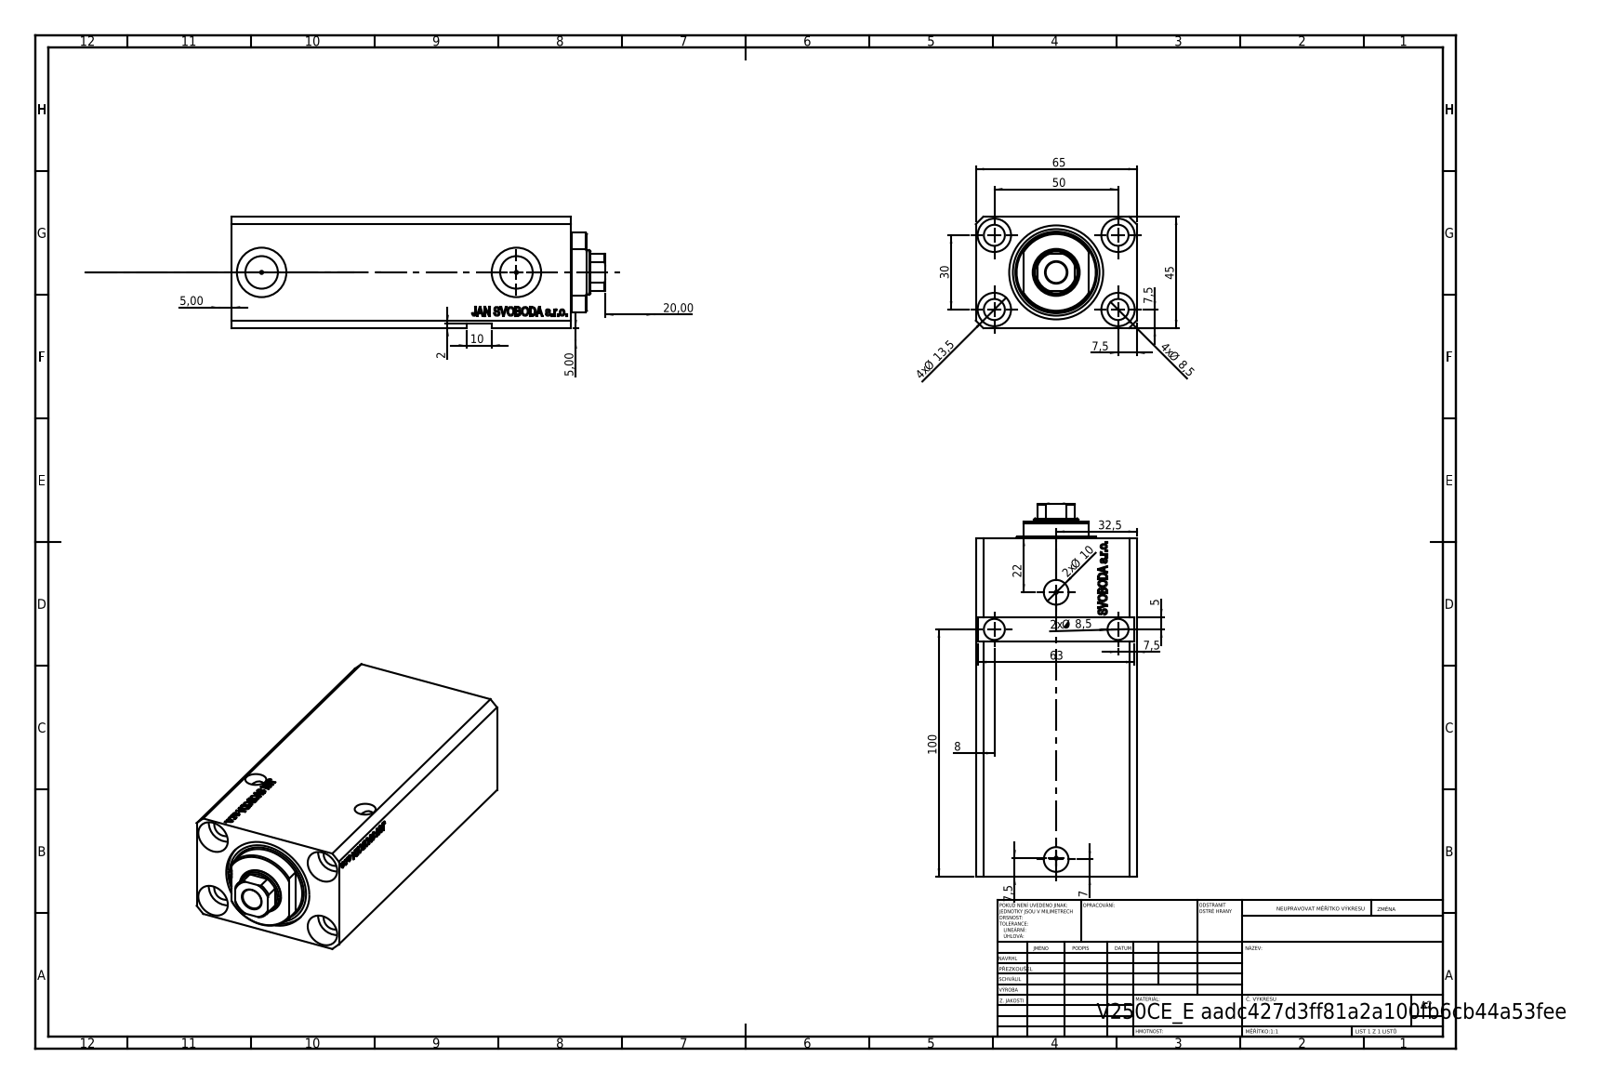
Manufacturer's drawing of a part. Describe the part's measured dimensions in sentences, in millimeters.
The part is named "V250CE_VC_E; V250CE_C_VCP; V250CE_E_Body". Its 3-D file was written by "SolidWorks 2019 (CONFIG_CONTROL_DESIGN)". It is 3 solids with 897 faces: 435 planar, 84 cylindrical and 378 other. Overall it measures 150.9 by 65 by 45 millimeters. Its volume is 338 321 cubic millimeters and its surface area 81 657 square millimeters. Round holes: 7 of diameter 8.5, 4 of diameter 1.25, 4 of diameter 13.5, 2 of diameter 10, 2 of diameter 13.16, 2 of diameter 20, 1 of diameter 18, 1 of diameter 25, 1 of diameter 38. Partial cylindrical surfaces (rounded edges, fillets, slot ends): 1 of radius 8.5, 1 of radius 16. The main face-to-face distances are 45, 65, 111.9, 137, 25.1, 6.9, 105, 130.1, 9, 128. The hole center spacings are 29.15, 50, 30, 58.31, 95.79, 96.3, 0.53, 103.
